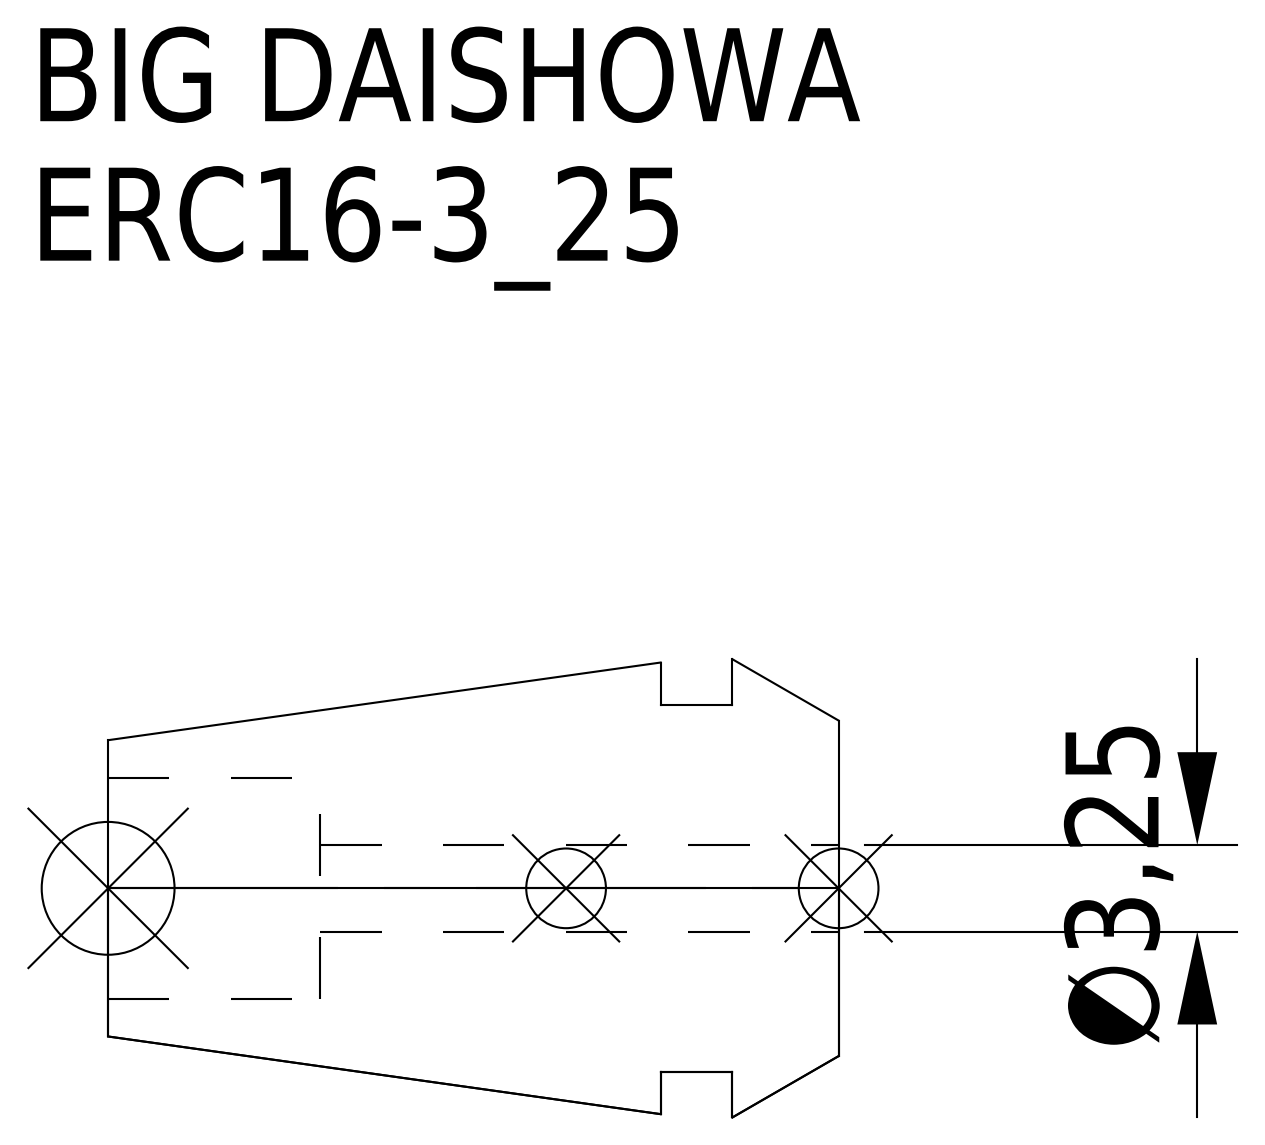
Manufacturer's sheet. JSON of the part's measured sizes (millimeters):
{"part_name": "ERC16-3_25", "step_written_by": "CREO PARAMETRIC BY PTC INC, 2016380 (AUTOMOTIVE_DESIGN)", "units": "millimeters", "bodies": {"solids": 1, "faces": 15, "planar": 5, "cylindrical": 6, "other": 4}, "overall_size": [27.5, 17.25, 17.25], "volume_mm3": 3801, "surface_area_mm2": 2038, "round_holes": [[3.25, 1], [8.3, 1]], "round_bosses_or_shafts": [[13.8, 1]], "face_to_face_distances": [4, 6.7, 2.7, 19.52, 15.52, 12.82, 27.5, 23.5, 20.8, 7.98]}
